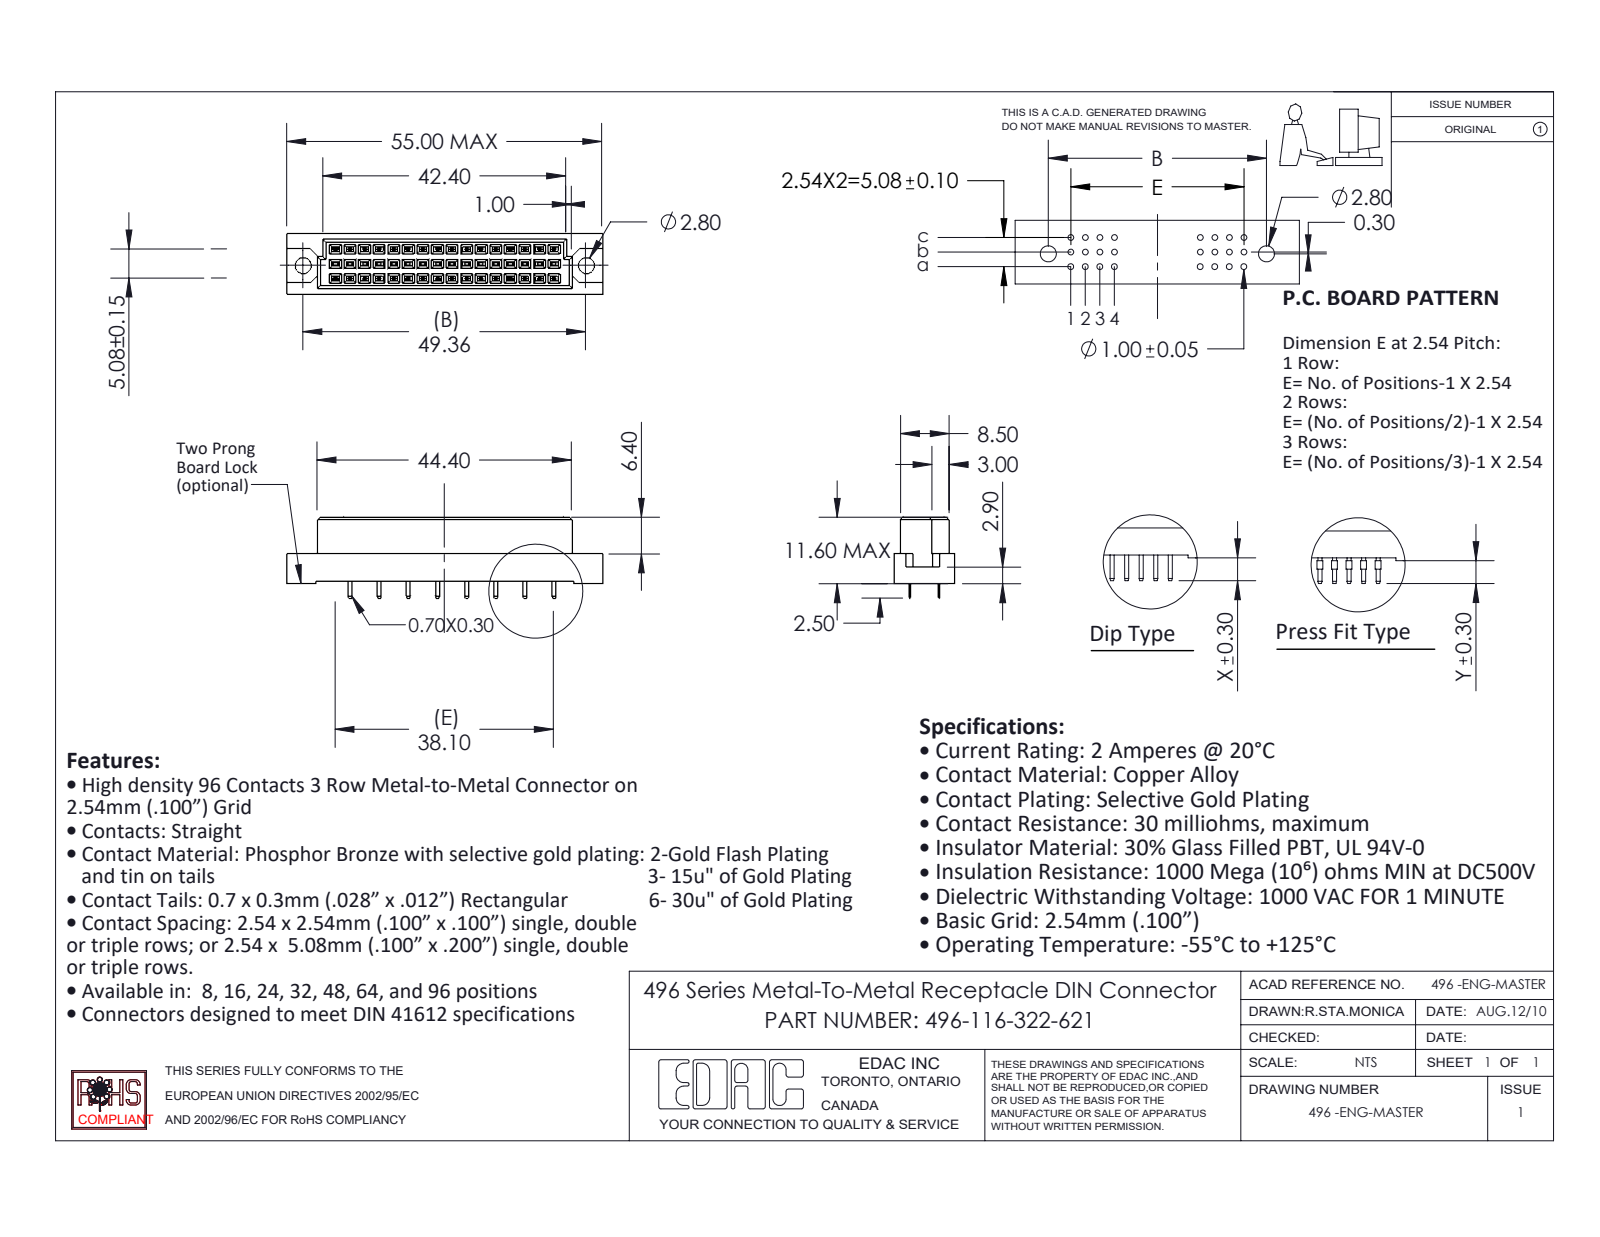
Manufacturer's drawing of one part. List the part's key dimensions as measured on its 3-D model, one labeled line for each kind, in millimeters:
Part name (STEP PRODUCT): 496-116-322-621; 496-290_22; 496 Part_48
STEP written by: SolidWorks 2020 (CONFIG_CONTROL_DESIGN)
Units: millimetres
Bodies: 17 solids, 826 faces (822 planar, 4 cylindrical, 0 other)
Overall size (bounding box): 55 × 14.1 × 10.6
Volume: 4 612 mm³ · Surface area: 4 439 mm²
Round holes (diameter × count): ⌀2.8 ×2
Main face-to-face distances: 2.54, 5.08, 1.05, 9.55, 0.81, 10.6, 3.35, 1.73, 8.5, 0.56
Hole centre spacings: 49.36
